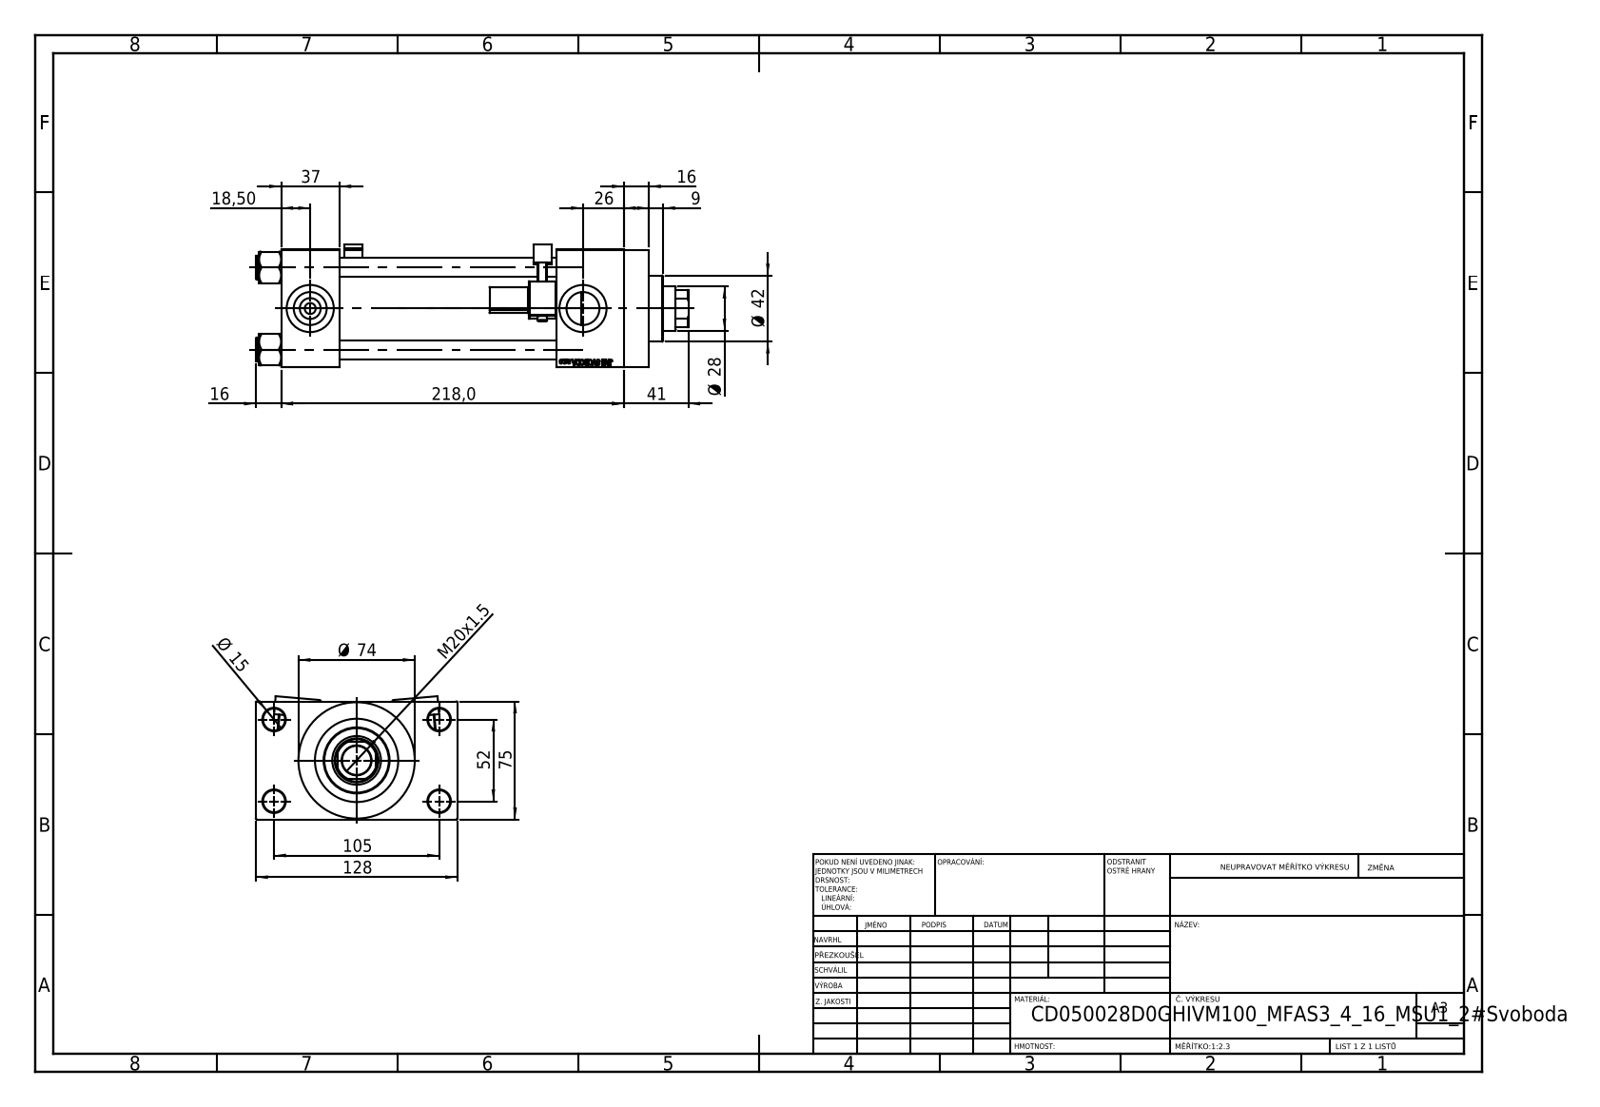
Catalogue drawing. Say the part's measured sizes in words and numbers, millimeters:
The part is named "V215CD_NUT_M5_D; V215CD_D_TYCINKA; V215CR_MSU; V215CD_VC_A (+2 more)". Its 3-D file was written by "SolidWorks 2019 (CONFIG_CONTROL_DESIGN)". It is 13 solids with 1257 faces: 555 planar, 148 cylindrical and 554 other. Overall it measures 275 by 128 by 78.34 millimeters. Its volume is 972 769 cubic millimeters and its surface area 228 618 square millimeters. Round holes: 4 of diameter 12, 4 of diameter 14, 2 of diameter 7, 2 of diameter 20.96, 2 of diameter 30, 1 of diameter 18.5, 1 of diameter 28, 1 of diameter 31, 1 of diameter 41, 1 of diameter 50, 1 of diameter 53. Round bosses or shafts: 4 of diameter 15, 2 of diameter 6, 1 of diameter 74, 1 of diameter 56, 1 of diameter 42. Partial cylindrical surfaces (rounded edges, fillets, slot ends): 48 of radius 0.5, 2 of radius 1, 2 of radius 2.5, 2 of radius 4, 1 of radius 13.5. The main face-to-face distances are 75, 138, 37, 175, 26.5, 101.5, 218, 181, 43, 16. The hole center spacings are 26.35, 36.98, 52.3, 58.43, 58.59, 78.65, 94.37, 52.
